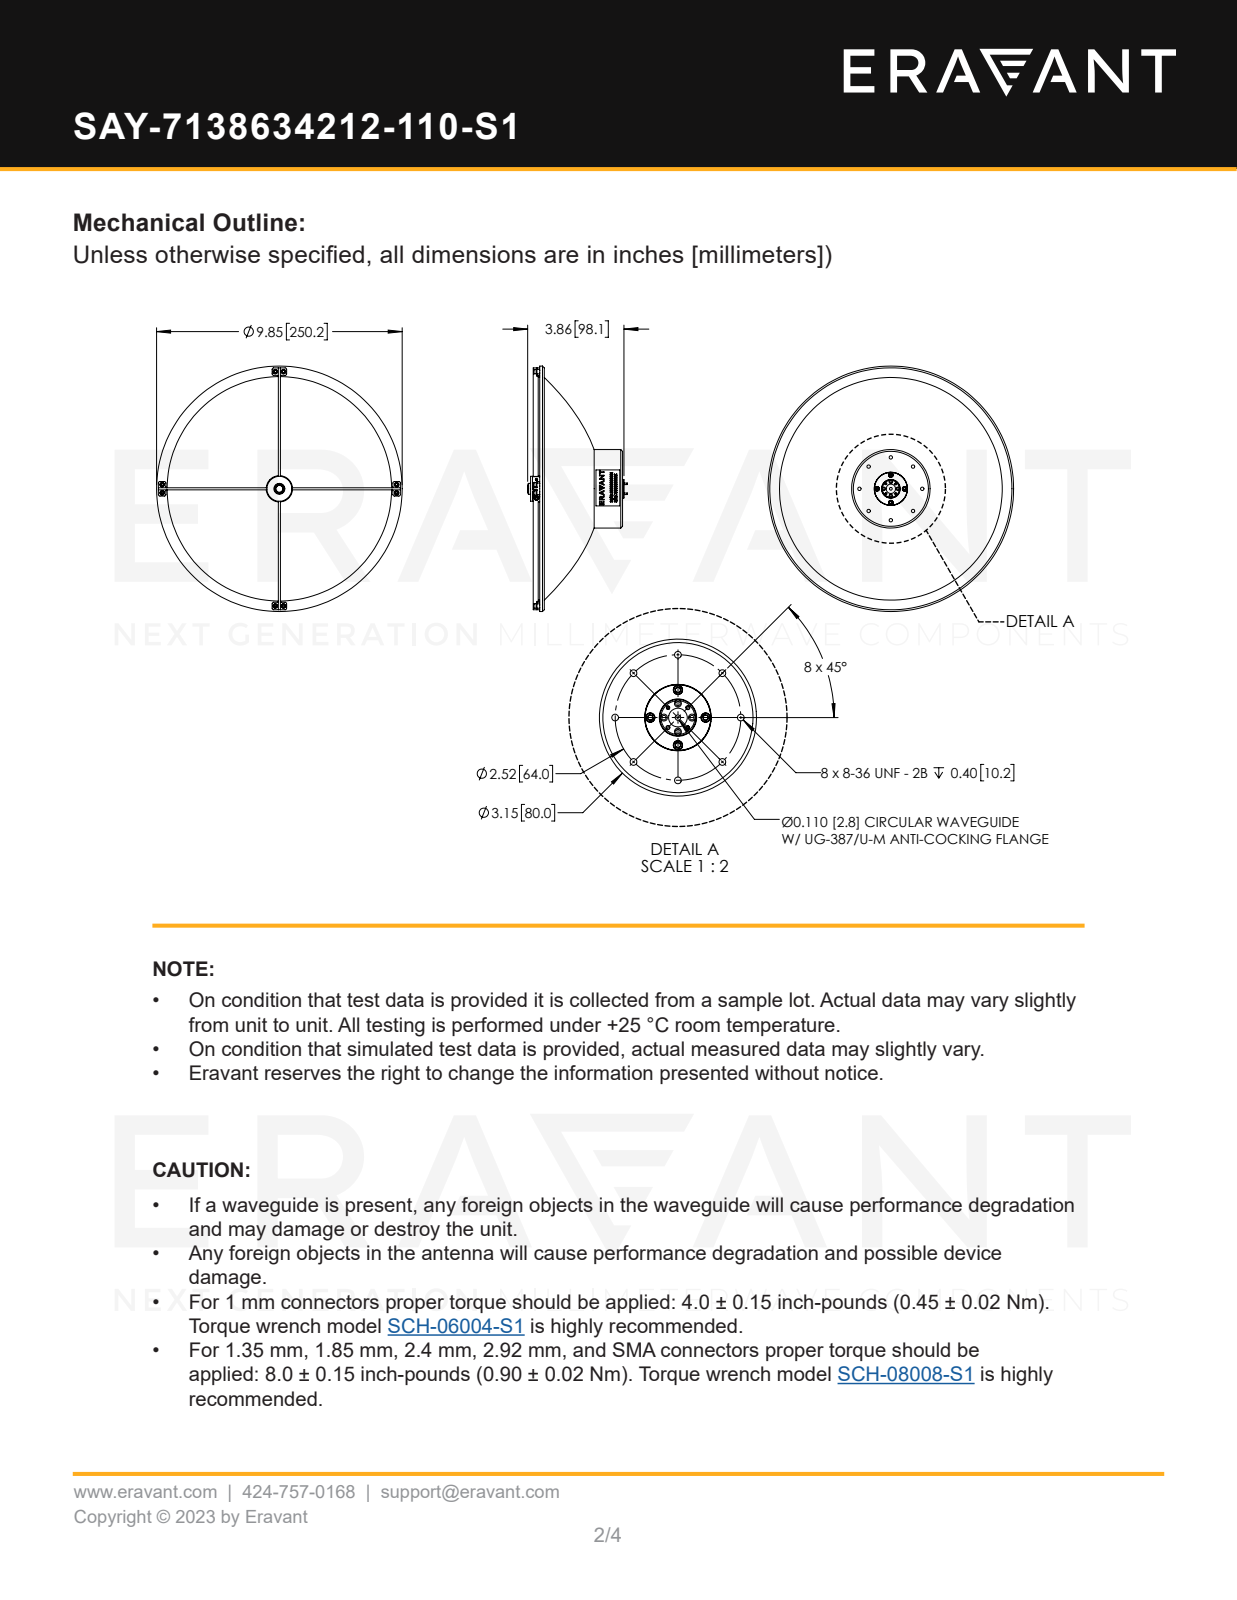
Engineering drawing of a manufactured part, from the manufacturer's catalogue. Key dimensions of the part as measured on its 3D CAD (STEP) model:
Part name (STEP PRODUCT): SAY-7138634212-110-S1
STEP written by: SolidWorks 2021 (CONFIG_CONTROL_DESIGN)
Units: inches
Bodies: 4 solids, 785 faces (347 planar, 154 cylindrical, 284 other)
Overall size (bounding box): 10.7 × 10.7 × 4.164
Volume: 146.9 in³ · Surface area: 268.6 in²
Round holes (diameter × count): ⌀0.096 ×16, ⌀0.136 ×8, ⌀0.089 ×4, ⌀0.14 ×4, ⌀0.188 ×4, ⌀0.061 ×2, ⌀0.067 ×2, ⌀0.11 ×1, ⌀0.68 ×1, ⌀1.335 ×1, ⌀10 ×1, ⌀10.3 ×1
Round bosses / shafts (diameter × count): ⌀0.086 ×16, ⌀0.183 ×4, ⌀0.063 ×2, ⌀10.7 ×1, ⌀10.641 ×1, ⌀10.29 ×1, ⌀3.15 ×1, ⌀1.325 ×1
Main face-to-face distances: 0.738, 0.838, 0.1, 3.137, 3.875, 3.975, 3.926, 0.789, 0.051, 0.049
Hole centre spacings: 2.048, 4.018, 4.991, 5.055, 5.149, 5.25, 5.257, 5.364
